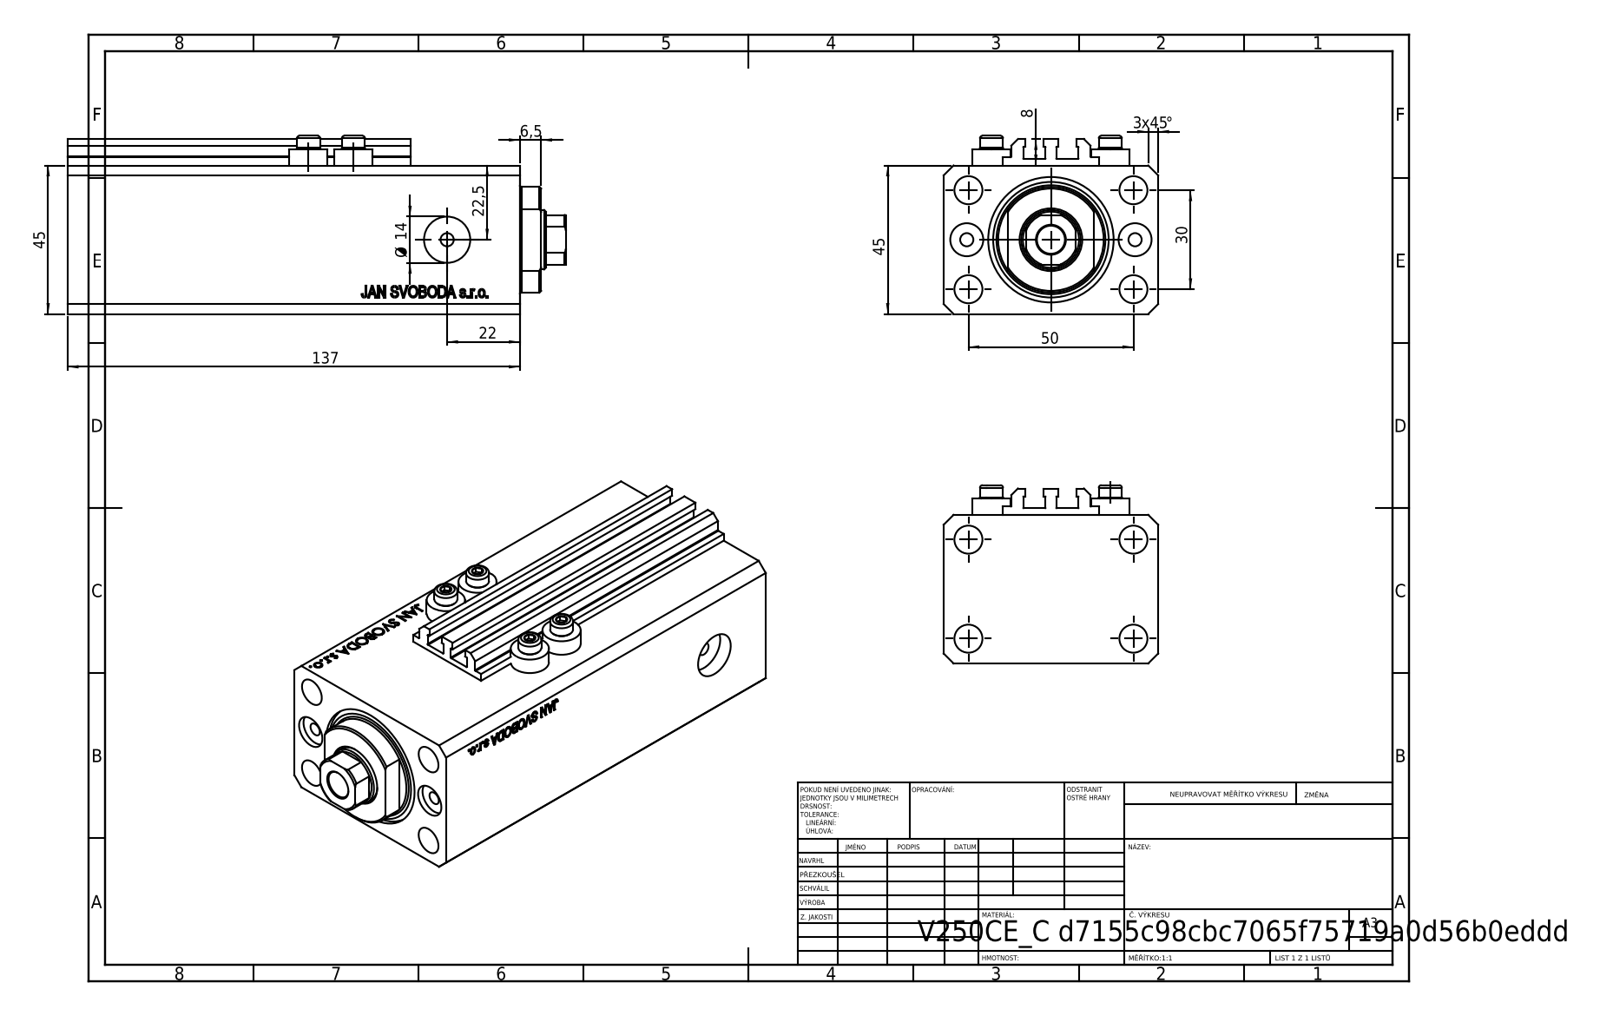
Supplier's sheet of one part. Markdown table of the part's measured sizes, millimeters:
| quantity | value |
| --- | --- |
| part name | V250CE_C_Body; V250CE_VC_C; ALLEN BOLT V250CE; V250CE_C_VCP |
| STEP written by | SolidWorks 2019 (CONFIG_CONTROL_DESIGN) |
| units | millimeters |
| bodies | 8 solids, 1033 faces (503 planar, 86 cylindrical, 444 other) |
| overall size | 150.9 × 65 × 54 |
| volume | 366 076 mm³ |
| surface area | 92 764 mm² |
| round holes (diameter × count) | 4 × 8, 8.5 × 5, 10 × 2, 14 × 2, 18 × 1, 25 × 1, 38 × 1 |
| round bosses / shafts (diameter × count) | 11.6 × 4, 7 × 4 |
| partial cylindrical surfaces (radius × count) | 0.2 × 10, 8.5 × 1, 16 × 1 |
| main face-to-face distances | 45, 65, 47, 111.9, 137, 25.1, 2.5, 2, 10, 73.52 |
| hole center spacings | 15.01, 29.15, 52.68, 13.6, 25.5, 30, 36, 38.48 |
